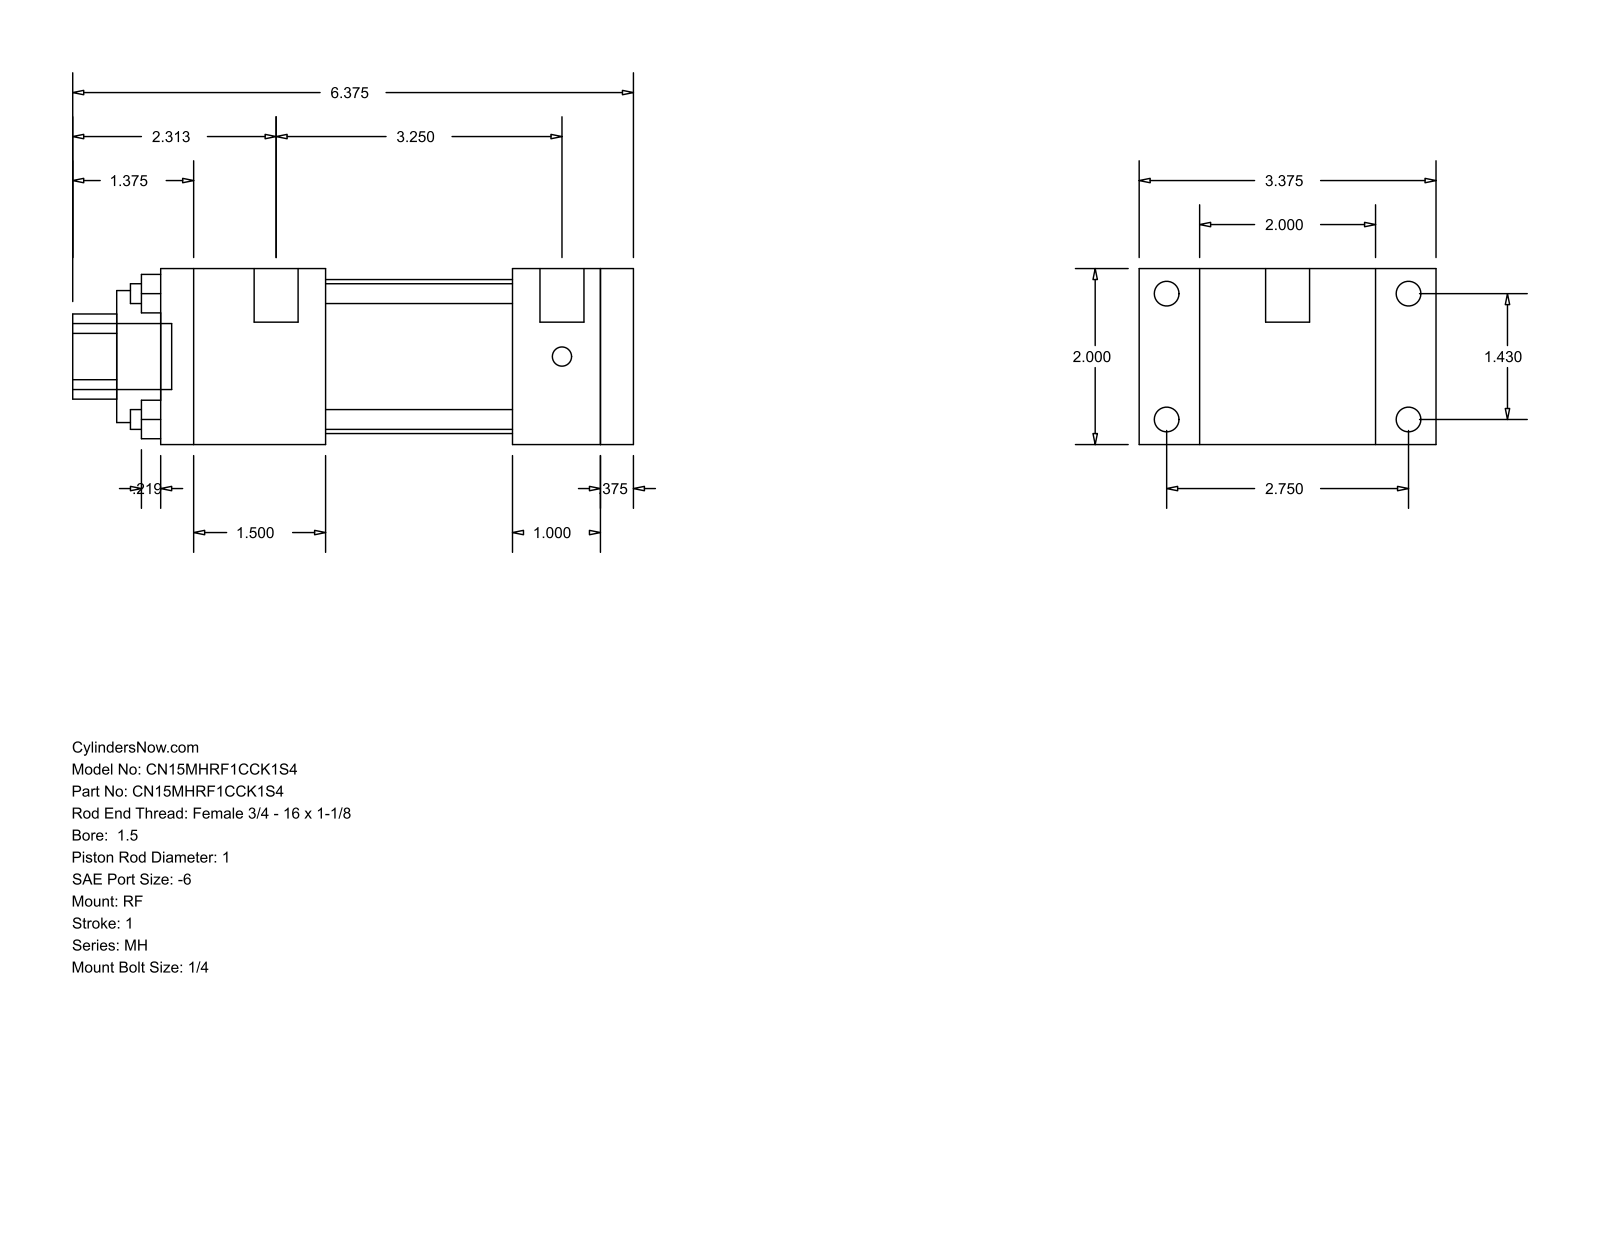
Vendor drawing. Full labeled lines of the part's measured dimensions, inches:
Part name (STEP PRODUCT): MH_RF__0150_1
STEP written by: GSSL Pune (CONFIG_CONTROL_DESIGN)
Units: inches
Bodies: 0 solids, 92 faces (64 planar, 28 cylindrical, 0 other)
Overall size (bounding box): 6.375 × 3.375 × 2
Round holes (diameter × count): ⌀0.225 ×4, ⌀1 ×1, ⌀1.5 ×1, ⌀1.75 ×1
Round bosses / shafts (diameter × count): ⌀0.281 ×4, ⌀0.219 ×4, ⌀0.5 ×2, ⌀0.75 ×1
Partial cylindrical surfaces — rounded edges, fillets, slot ends (radius × count): R0.484 ×1
Main face-to-face distances: 2, 0.375, 5, 1, 5.375, 0.687, 2.687, 4, 1.375, 1.875
Hole centre spacings: 1.011, 1.43, 2.022
